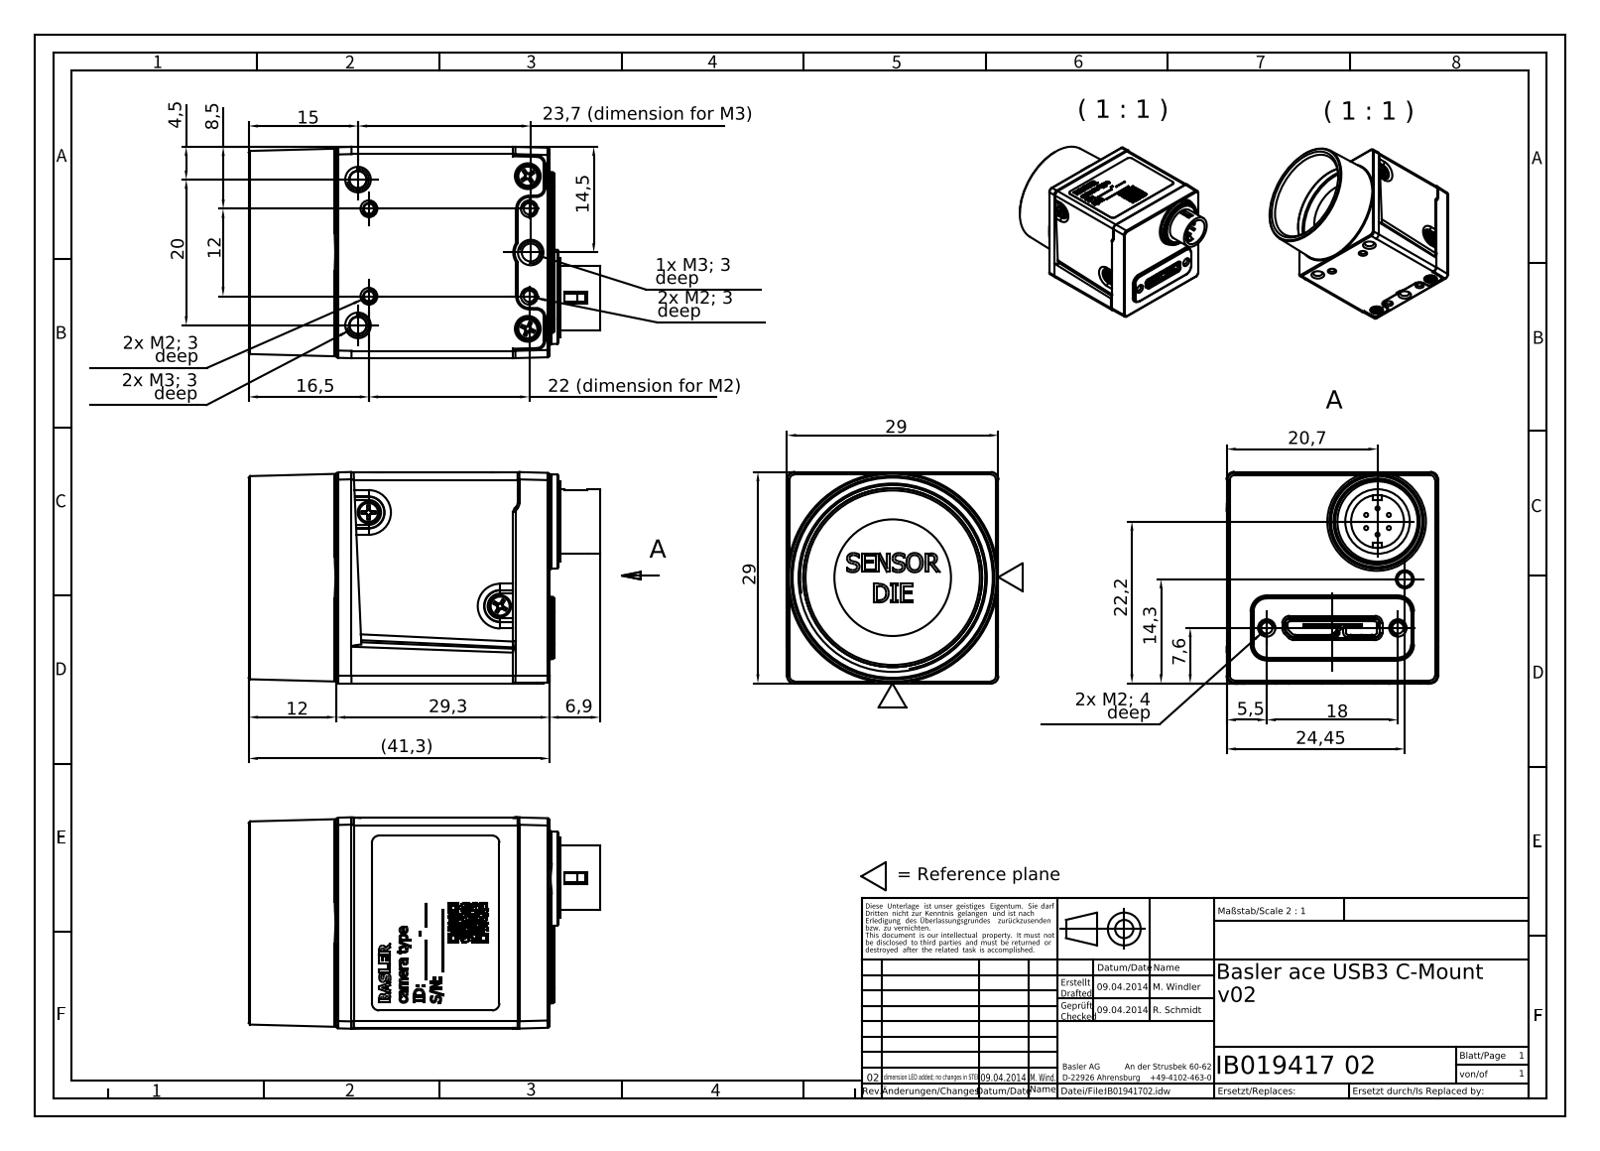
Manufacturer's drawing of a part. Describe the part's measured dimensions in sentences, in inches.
The part is named "139705407318IP01941702". Its 3-D file was written by "Autodesk Inventor 2011 (AUTOMOTIVE_DESIGN)". It is 3 solids with 1315 faces: 831 planar, 185 cylindrical and 299 other. Overall it measures 1.898 by 1.142 by 1.142 inches. Its volume is 1.545 cubic inches and its surface area 12.8 square inches. Round holes: 6 of diameter 0.062, 2 of diameter 0.035, 2 of diameter 0.073, 2 of diameter 0.097, 1 of diameter 0.097, 1 of diameter 0.285, 1 of diameter 0.63, 1 of diameter 0.966. Round bosses or shafts: 6 of diameter 0.022, 5 of diameter 0.118, 5 of diameter 0.056, 3 of diameter 0.063, 2 of diameter 0.043, 1 of diameter 0.433, 1 of diameter 0.348. Partial cylindrical surfaces (rounded edges, fillets, slot ends): 28 of radius 0.039, 22 of radius 0.008, 20 of radius 0.012, 14 of radius 0.004, 8 of radius 0.02, 7 of radius 0.026, 5 of radius 0.028, 4 of radius 0.014. The main face-to-face distances are 1.134, 1.14, 1.138, 1.169, 0.233, 0.936, 0.024, 0.016, 1.193, 0.959. The hole center spacings are 0.168, 0.236, 0.472, 0.633, 0.866, 0.906, 0.939, 0.987.
